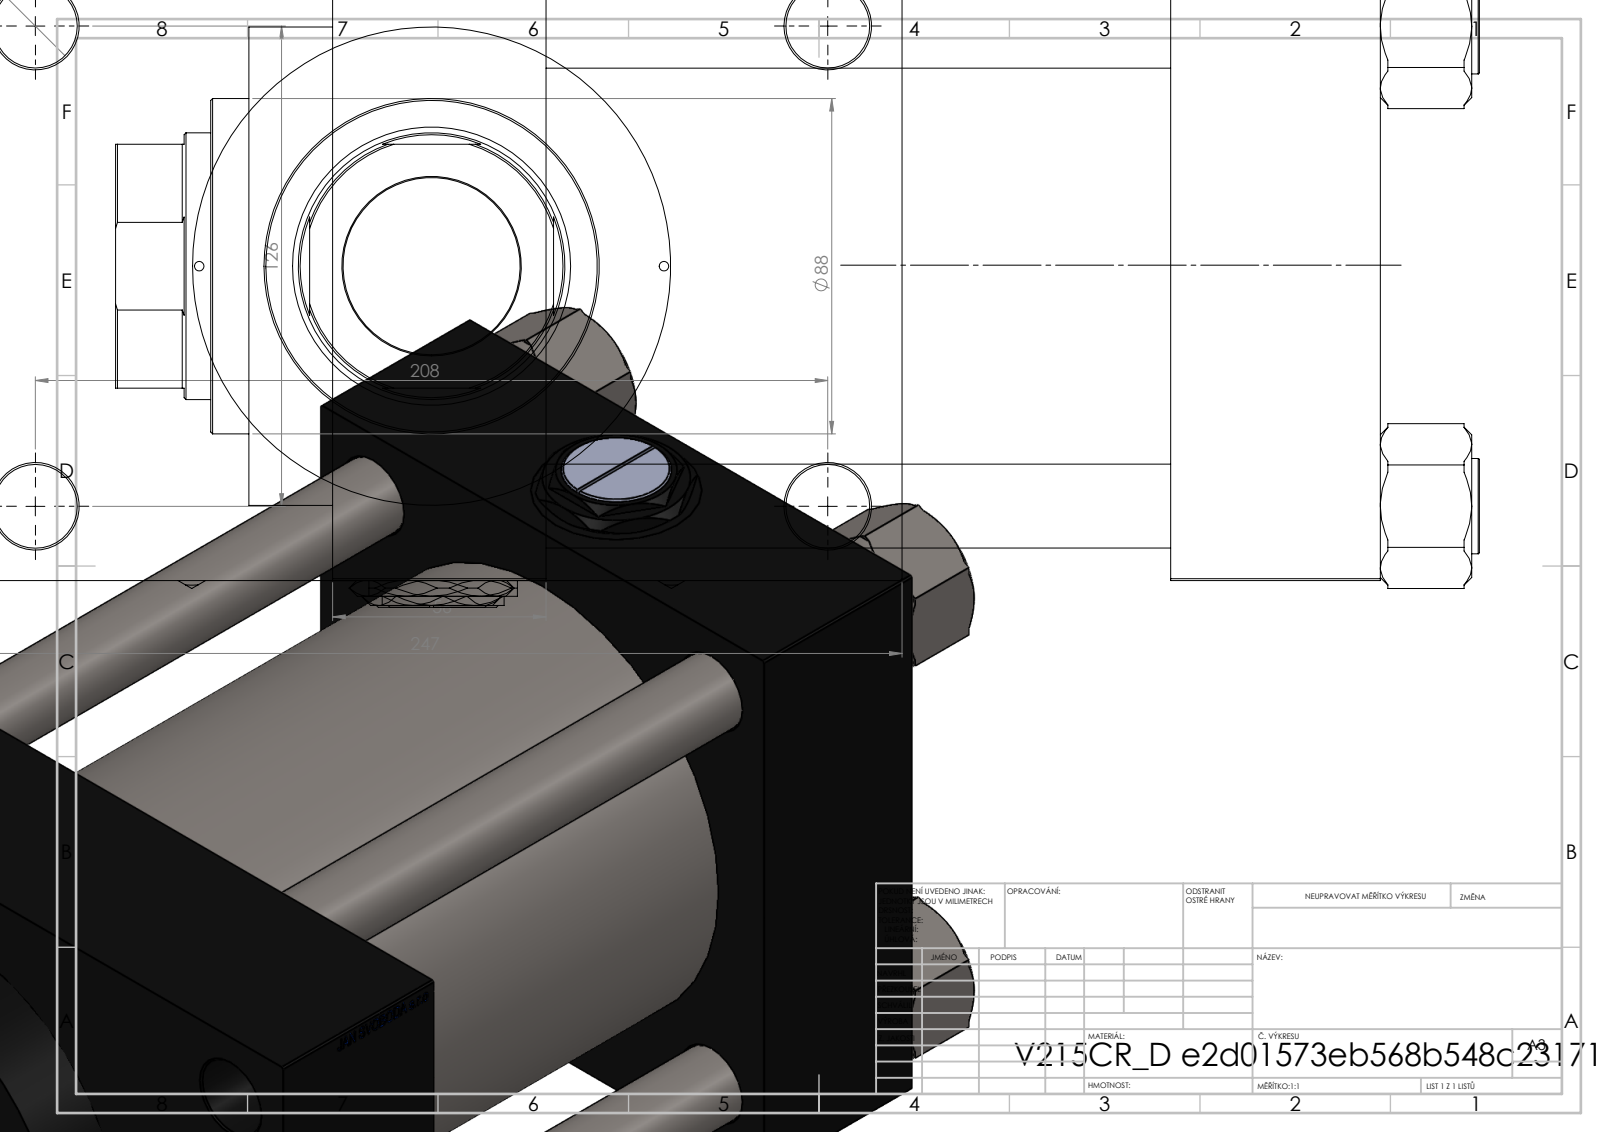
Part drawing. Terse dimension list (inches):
name: V215CR_D_TYCINKA; Zatka_pro_OIL_PORT; NUT_M5_D; V215CR_D_Body (+2 more)
written by: SolidWorks 2019 (CONFIG_CONTROL_DESIGN)
unit: in
bodies: 13 solids, 1239 faces (590 planar, 91 cylindrical, 558 other)
size: 14.094 × 9.724 × 7.047
volume: 341 in³; area: 1 006 in²
holes: 8× ⌀0.866, 2× ⌀0.098, 2× ⌀0.276, 2× ⌀1.269, 2× ⌀1.772, 1× ⌀1.831, 1× ⌀2.756, 1× ⌀2.874, 1× ⌀3.78, 1× ⌀4.921, 1× ⌀4.941
bosses: 4× ⌀0.984, 1× ⌀5.157, 1× ⌀3.465
rounds: 1× R1.339
face distances: 6.496, 6.457, 2.165, 8.622, 2.205, 10.827, 8.661, 1.614, 8.11, 9.99
hole spacings: 1.616, 2.48, 3.003, 3.505, 4.787, 4.957, 5.215, 5.473
